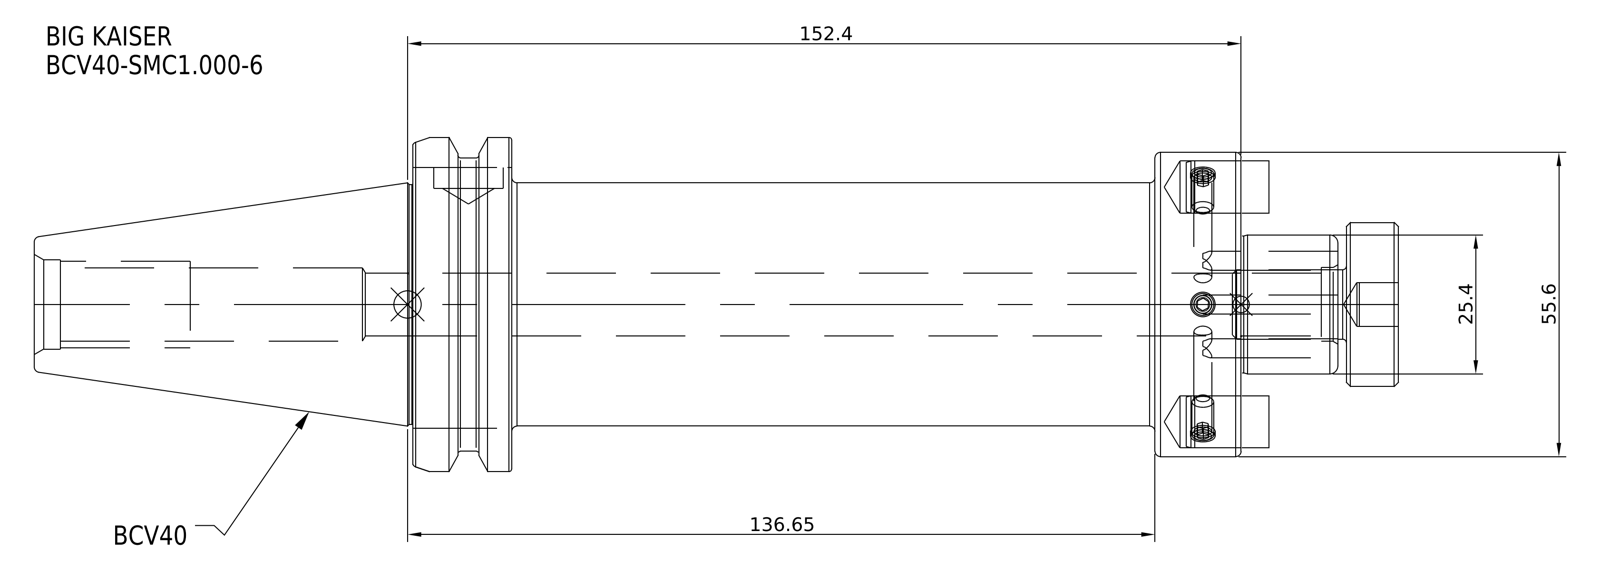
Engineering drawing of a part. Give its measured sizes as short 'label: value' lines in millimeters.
name: BCV40-SMC1_000-6
written by: SolidWorks 2021 (CONFIG_CONTROL_DESIGN)
unit: mm
bodies: 1 solid, 38 faces (18 planar, 14 cylindrical, 6 other)
size: 225.55 × 63.5 × 63.5
volume: 330 238 mm³; area: 42 796 mm²
holes: 1× ⌀11.51
bosses: 1× ⌀63.5, 1× ⌀56.36, 1× ⌀55.6, 1× ⌀44.45
face distances: 151.4, 133.35, 18.05, 15.75, 117.6, 135.65, 220.65, 204.9, 87.3, 69.25
